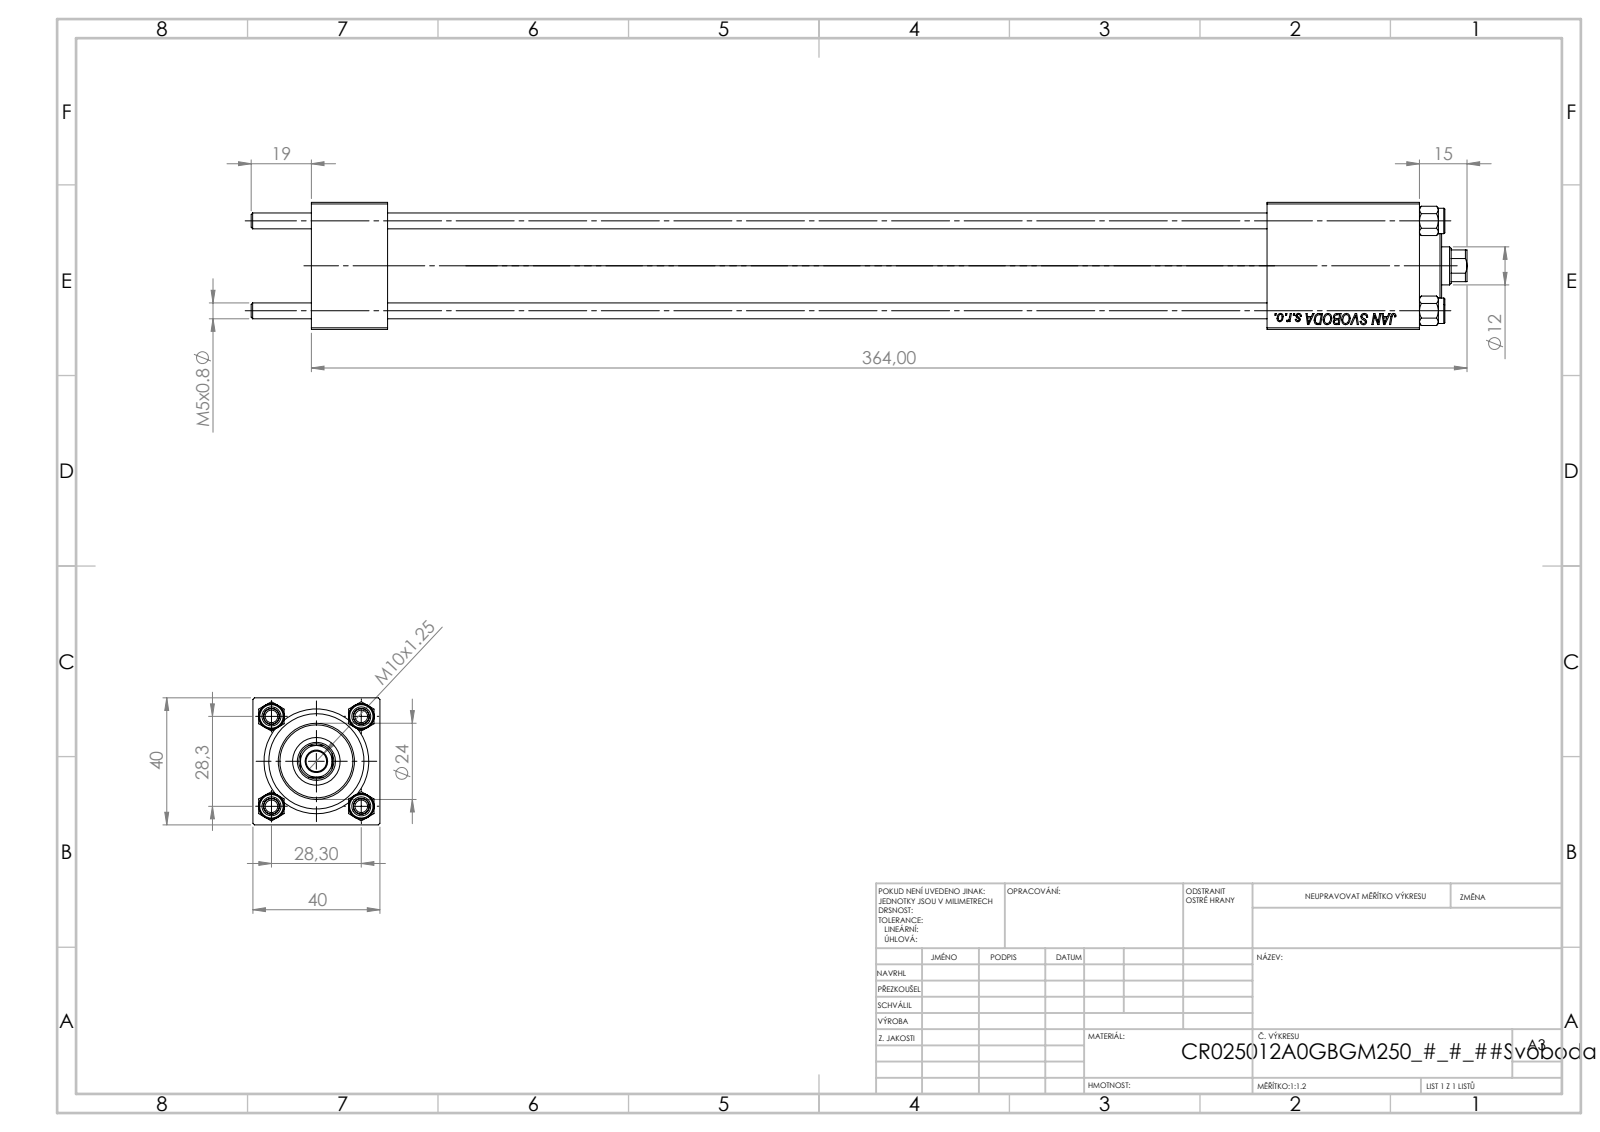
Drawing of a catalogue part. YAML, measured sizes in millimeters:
part_name: "NUT_M5; CR025_012_A_0_G_A_G_M_020_+#_##_TYCINKA; V215_VC_A; V215CR_VCP (+1 more)"
step_written_by: "SolidWorks 2019 (CONFIG_CONTROL_DESIGN)"
units: millimeters
bodies: {solids: 11, faces: 1131, planar: 517, cylindrical: 78, other: 536}
overall_size: [383, 40, 40]
volume: 249848
surface_area: 122392
round_holes:
  - {diameter: 5, count: 4}
  - {diameter: 20, count: 3}
  - {diameter: 7, count: 2}
  - {diameter: 13.16, count: 2}
  - {diameter: 6.5, count: 1}
  - {diameter: 12, count: 1}
  - {diameter: 15, count: 1}
  - {diameter: 25, count: 1}
  - {diameter: 30, count: 1}
round_bosses_or_shafts:
  - {diameter: 8, count: 4}
  - {diameter: 31, count: 1}
  - {diameter: 24, count: 1}
partial_cylinders:
  - {radius: 5.5, count: 1}
face_to_face_distances: [40, 24, 349, 325, 320.3, 296.3, 28.7, 301, 277, 19.3]
hole_center_spacings: [20.01, 28.3, 40.02, 302]
